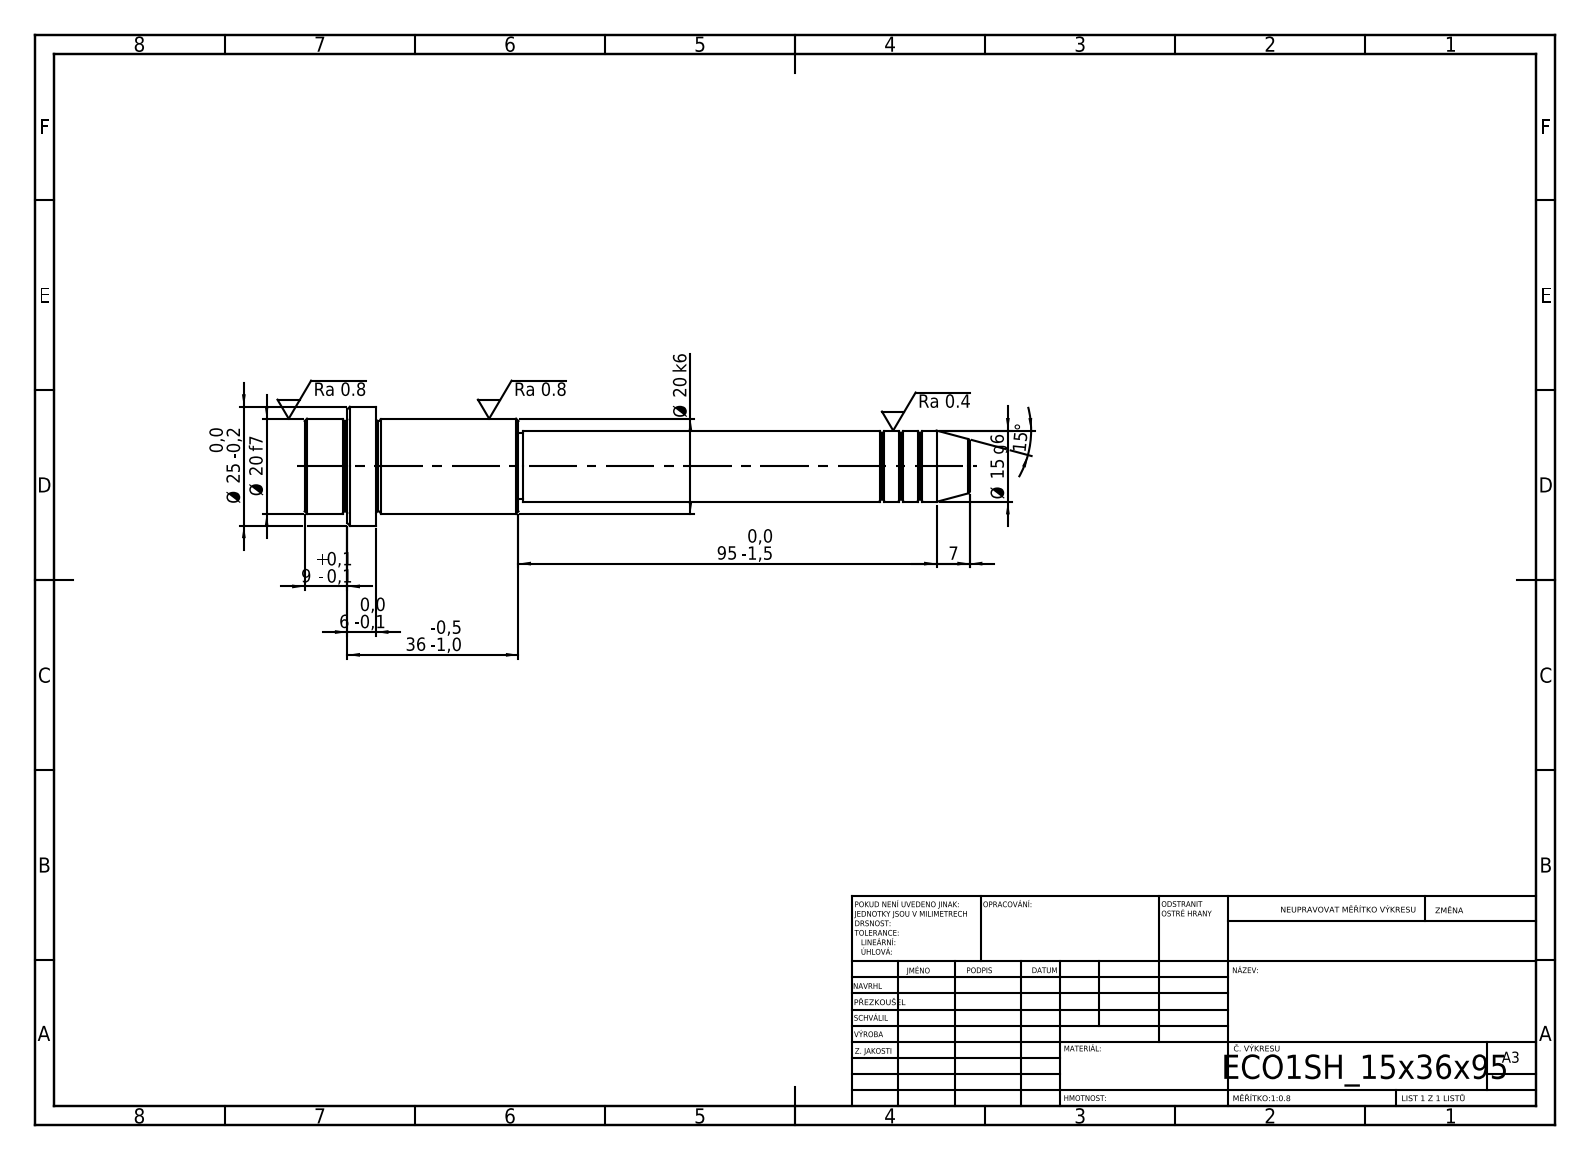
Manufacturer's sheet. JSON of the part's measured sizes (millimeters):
{"step_written_by": "SolidWorks 2019 (CONFIG_CONTROL_DESIGN)", "units": "millimeters", "bodies": {"solids": 1, "faces": 52, "planar": 6, "cylindrical": 16, "other": 30}, "overall_size": [140, 25, 25], "volume_mm3": 31551, "surface_area_mm2": 8386, "round_bosses_or_shafts": [[25, 1], [20, 1], [15, 1], [14, 1]], "face_to_face_distances": [15, 6, 9, 30, 36, 45, 95, 125, 131, 140]}
